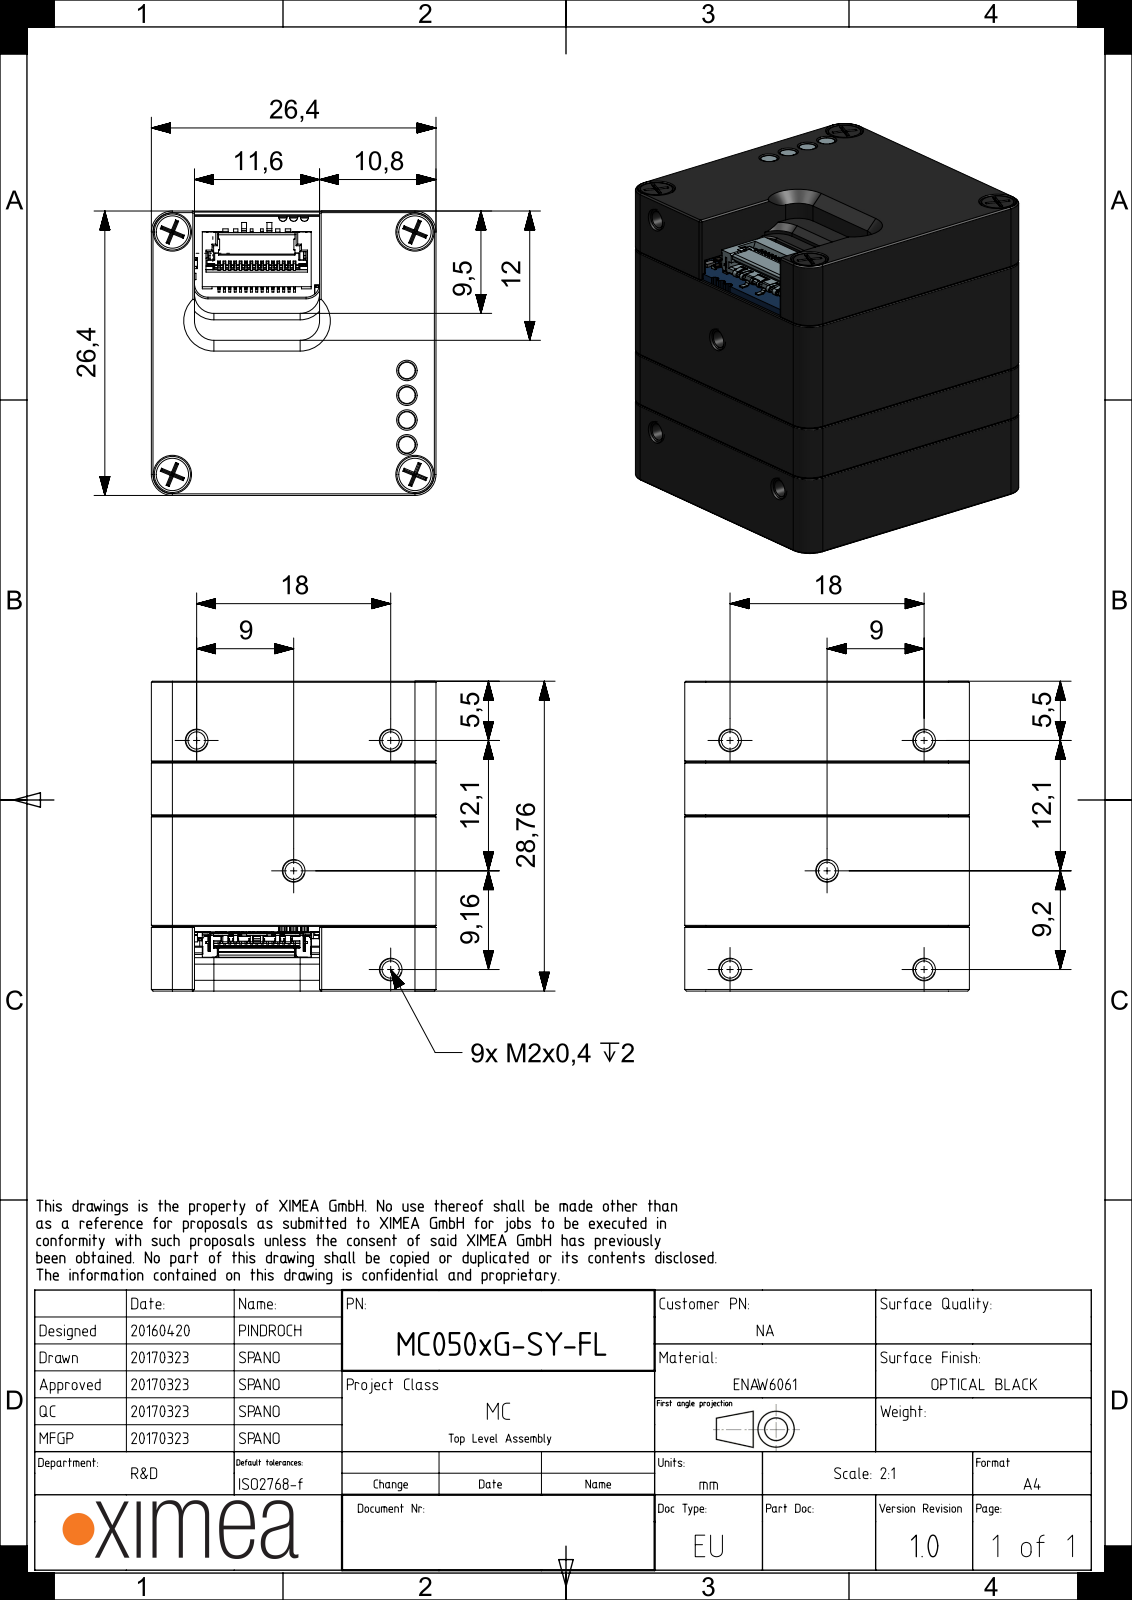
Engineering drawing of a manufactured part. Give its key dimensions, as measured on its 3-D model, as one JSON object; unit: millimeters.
{"part_name": "MECH-O-RING-22X1-VI370; MT050xG-PR-SENSOR-PCA; FLT-BK7-AR2X-D25; SROB-M1.6x3-SLOT-STNLS (+8 more)", "step_written_by": "SIEMENS PLM Software NX 1907 (AUTOMOTIVE_DESIGN)", "units": "millimeters", "bodies": {"solids": 32, "faces": 7200, "planar": 4889, "cylindrical": 2020, "other": 291}, "overall_size": [28.8, 26.4, 26.4], "volume_mm3": 9800, "surface_area_mm2": 16850, "round_holes": [[1.6, 13], [1, 4], [1.8, 4], [2, 4], [2.1, 4], [3, 4], [3.2, 4], [3.4, 4], [1.3, 2], [1.9, 1], [1.9, 1], [4, 1]], "round_bosses_or_shafts": [[1.9, 4], [1.6, 4], [0.8, 4], [3, 2], [1.6, 2], [25, 1], [21.6, 1]], "partial_cylinders_radius": [[1, 26], [0.3, 17], [0.1, 14], [0.2, 14], [0.2, 12], [0.4, 12], [1.5, 12], [1.3, 8]], "face_to_face_distances": [1, 3.5, 26.4, 6.9, 7.7, 4.2, 4.5, 11.4, 6.8, 10.4], "hole_center_spacings": [3.8, 12.9, 15.9, 18.8, 22.1, 22.5, 28.7, 2.3]}
